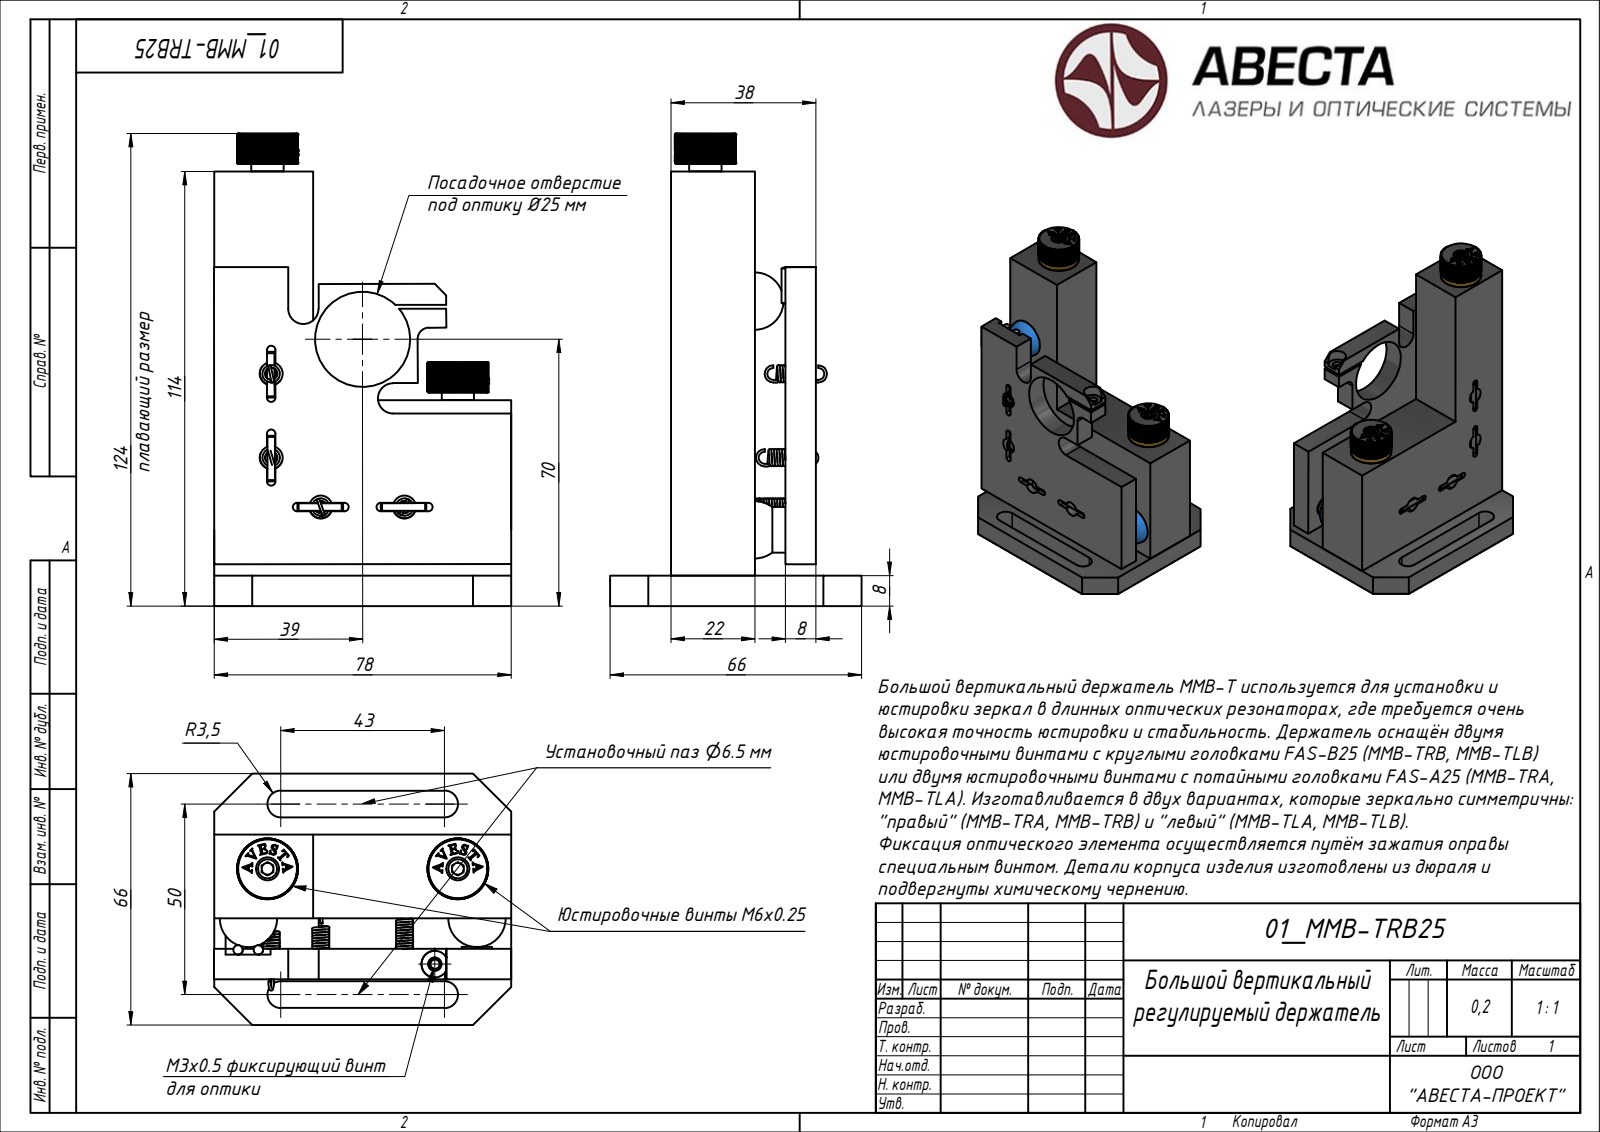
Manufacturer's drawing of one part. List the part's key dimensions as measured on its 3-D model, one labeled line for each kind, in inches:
STEP written by: ST-DEVELOPER v15 (AUTOMOTIVE_DESIGN)
Units: inches
Bodies: 46 solids, 1141 faces (540 planar, 0 cylindrical, 601 other)
Overall size (bounding box): 7.402 × 4.889 × 2.598
Volume: 21.23 in³ · Surface area: 185.7 in²
Main face-to-face distances: 0.315, 0.63, 1.496, 0.866, 1.181, 4.328, 0.307, 0.322, 1.811, 2.126
